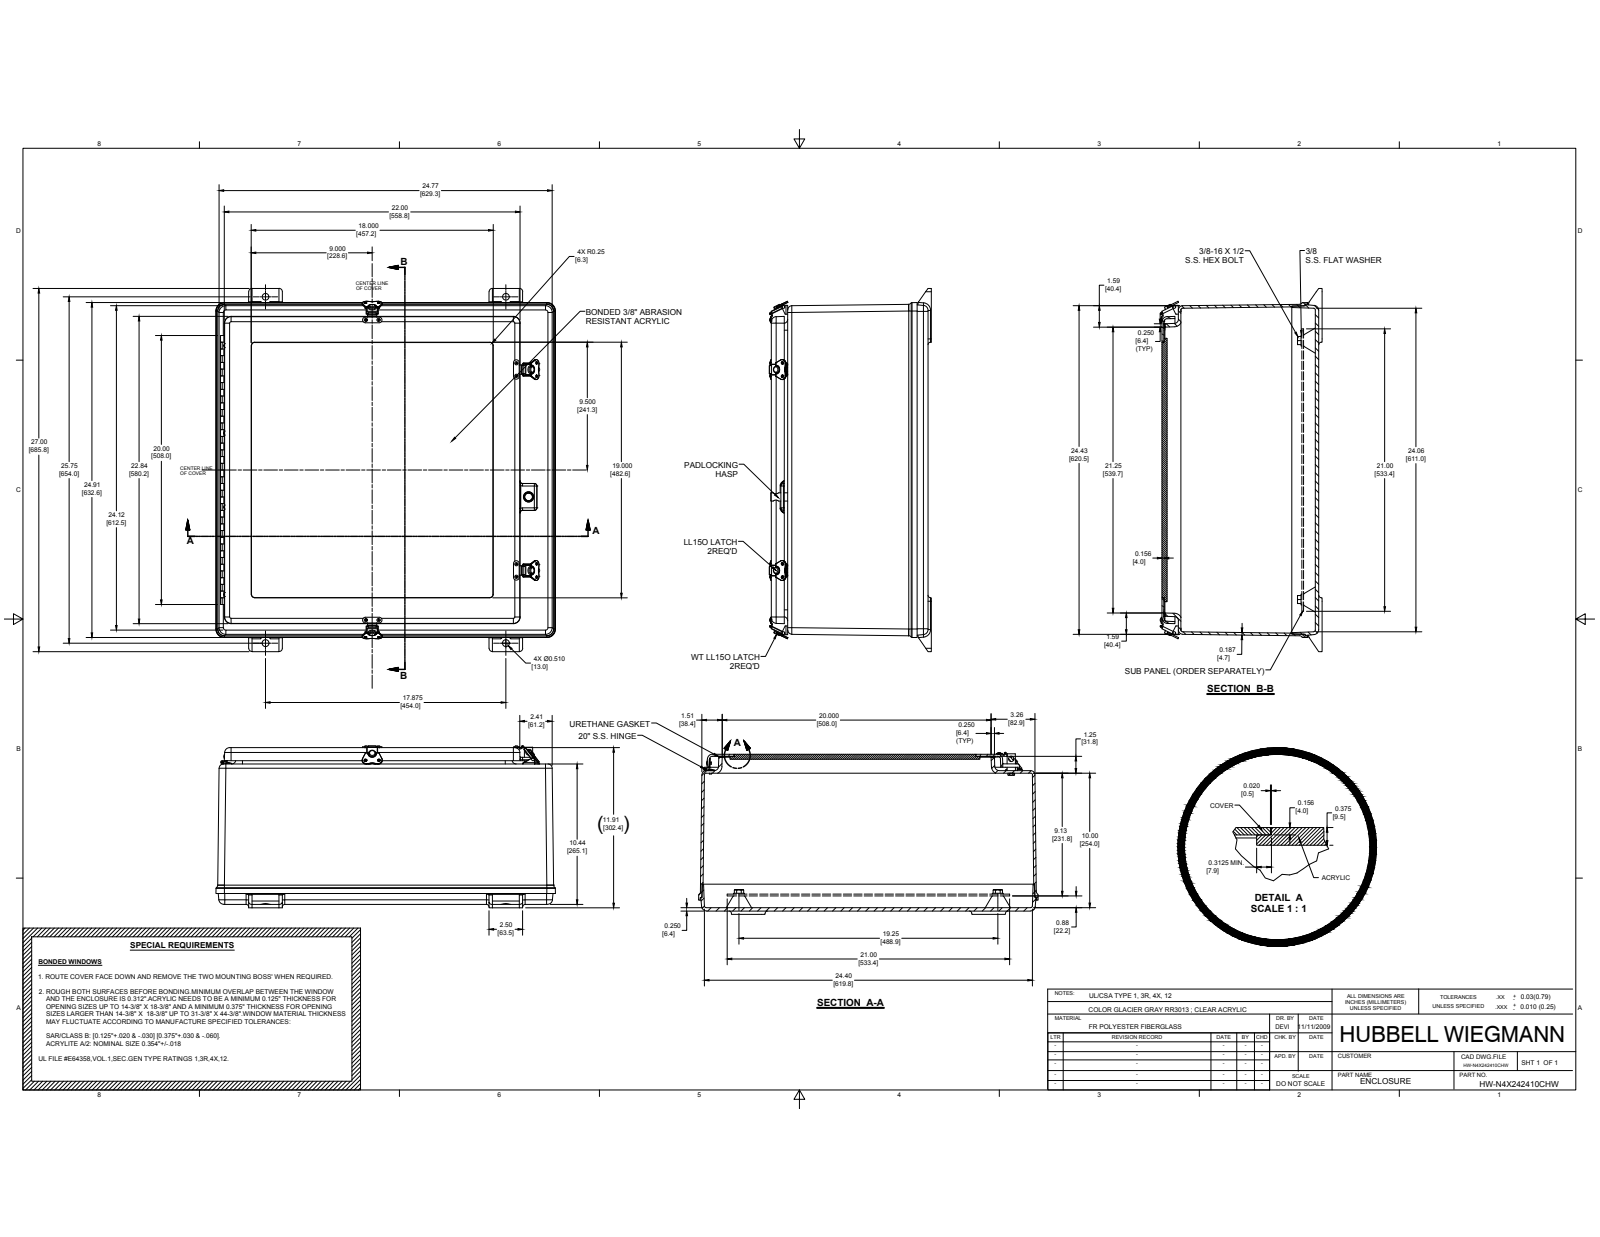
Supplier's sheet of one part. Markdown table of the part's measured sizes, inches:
| quantity | value |
| --- | --- |
| part name | WPN2424B; WPN242410SHWT; SS HINGE COVER (20); 0.13 RIVET PIN (+7 more) |
| STEP written by | Autodesk Inventor 2014 (AUTOMOTIVE_DESIGN) |
| units | inches |
| bodies | 59 solids, 1592 faces (617 planar, 614 cylindrical, 361 other) |
| overall size | 27 × 25.25 × 12.056 |
| volume | 584 in³ |
| surface area | 5 428 in² |
| round holes (diameter × count) | 0.13 × 32, 0.063 × 16, 0.065 × 8, 0.138 × 8, 0.187 × 8, 0.307 × 4, 0.563 × 4, 0.135 × 3, 0.156 × 3, 0.5 × 2, 0.51 × 2, 0.125 × 1 |
| round bosses / shafts (diameter × count) | 0.14 × 16, 0.297 × 8, 0.5 × 4, 0.2 × 3, 0.25 × 1, 0.201 × 1 |
| partial cylindrical surfaces (radius × count) | 0.01 × 101, 0.25 × 28, 0.187 × 21, 0.03 × 16, 0.313 × 16, 0.375 × 12, 0.5 × 12, 0.063 × 10 |
| main face-to-face distances | 0.187, 0.25, 11.659, 11.409, 11.284, 11.034, 0.375, 0.156, 0.219, 11.503 |
| hole center spacings | 6.5, 12, 23.032, 0.751, 0.937, 1, 1.512, 3.322 |
